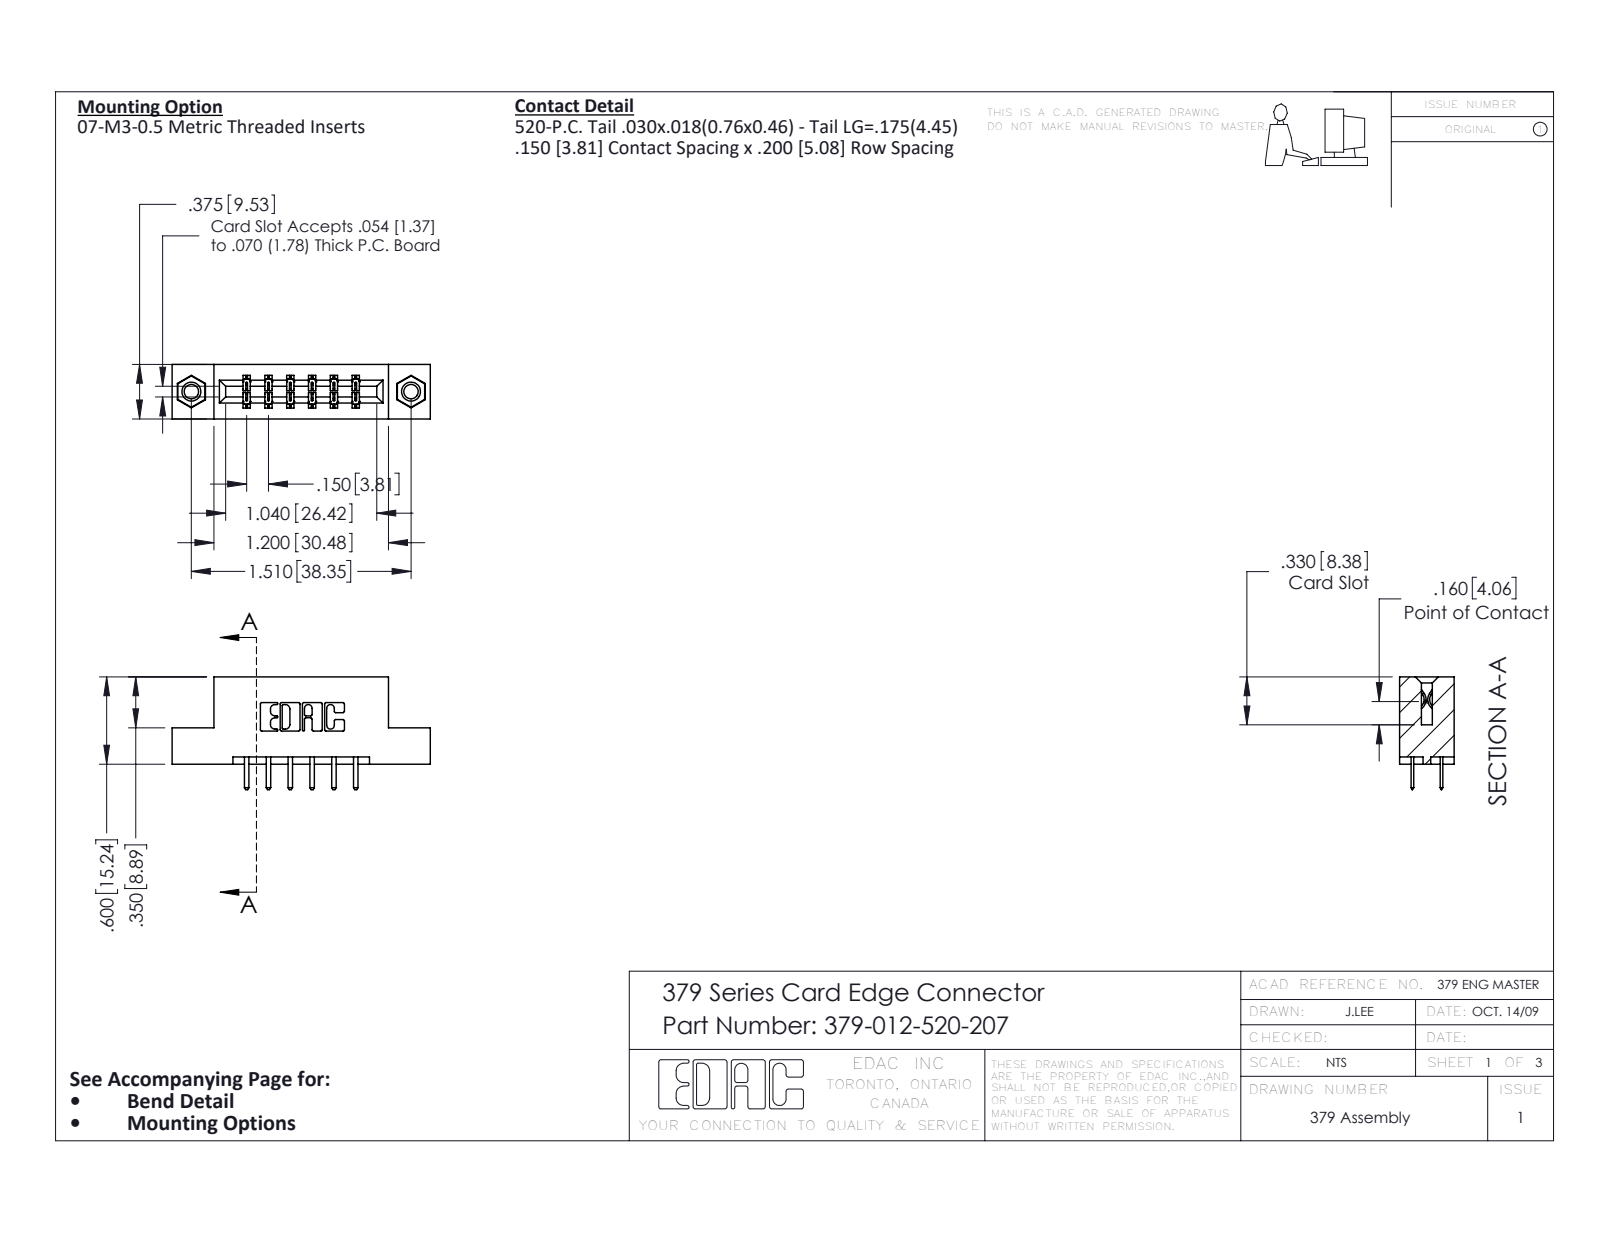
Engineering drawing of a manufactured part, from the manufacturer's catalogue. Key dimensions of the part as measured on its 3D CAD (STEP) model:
Part name (STEP PRODUCT): 379-012-520-207; 345-250-001_345-250-005-103; 379 Part_Flush - .156 Dia - TI; 345-292-001_345-293-120
STEP written by: SolidWorks 2016 (CONFIG_CONTROL_DESIGN)
Units: inches
Bodies: 15 solids, 846 faces (558 planar, 272 cylindrical, 16 other)
Overall size (bounding box): 1.775 × 0.775 × 0.375
Volume: 0.264 in³ · Surface area: 7.055 in²
Round holes (diameter × count): ⌀0.098 ×2, ⌀0.125 ×2, ⌀0.156 ×2
Round bosses / shafts (diameter × count): ⌀0.155 ×2
Partial cylindrical surfaces — rounded edges, fillets, slot ends (radius × count): R0.01 ×22, R0.006 ×18, R0.01 ×16, R0.007 ×6, R0.031 ×6, R0.026 ×3, R0.014 ×2, R0.022 ×2
Main face-to-face distances: 0.3, 0.2, 0.05, 0.15, 0.375, 0.25, 0.35, 0.1, 0.075, 0.55
Hole centre spacings: 1.51
